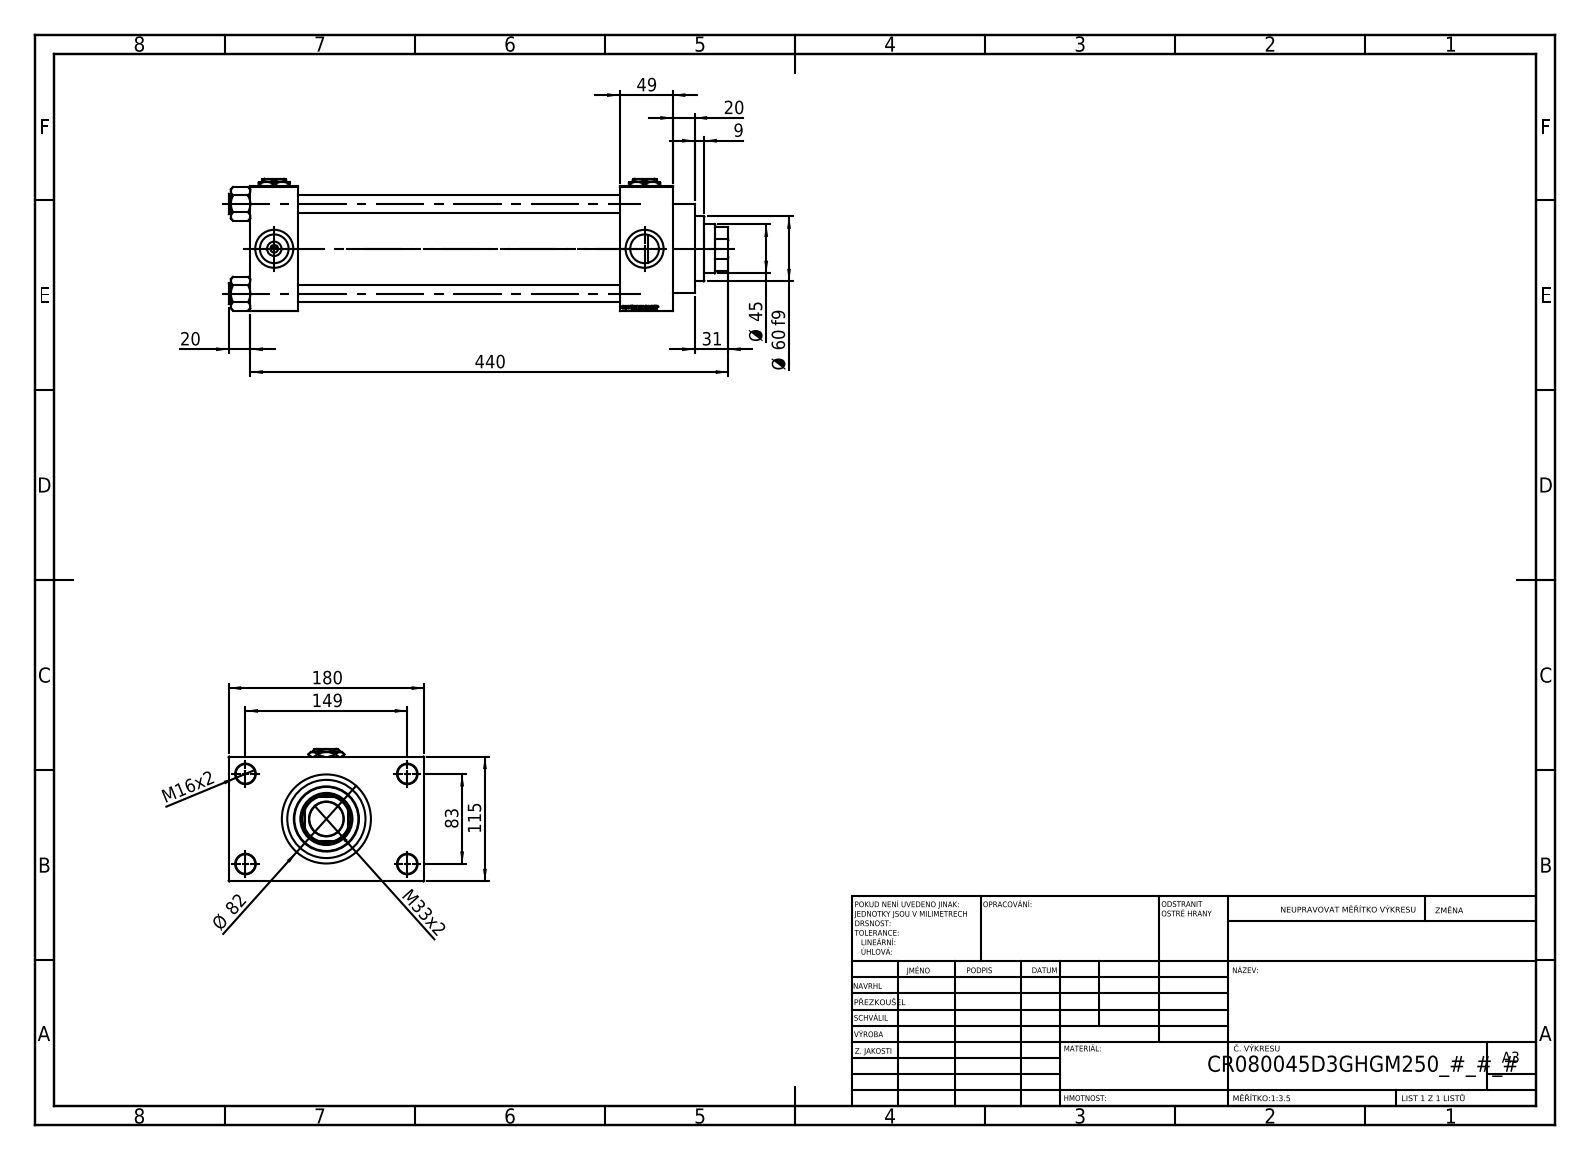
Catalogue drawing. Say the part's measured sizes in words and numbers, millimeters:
The part is named "V215_VC_A; Zatka_pro_OIL_PORT; V215CR_VCP_D; NUT_M5_D (+2 more)". Its 3-D file was written by "SolidWorks 2019 (CONFIG_CONTROL_DESIGN)". It is 13 solids with 1252 faces: 593 planar, 99 cylindrical and 560 other. Overall it measures 460 by 180 by 122 millimeters. Its volume is 2 721 000 cubic millimeters and its surface area 507 865 square millimeters. Round holes: 4 of diameter 16, 4 of diameter 18, 4 of diameter 26.44, 4 of diameter 35, 3 of diameter 7, 1 of diameter 31.5, 1 of diameter 45, 1 of diameter 48, 1 of diameter 61, 1 of diameter 72, 1 of diameter 80. Round bosses or shafts: 4 of diameter 19, 1 of diameter 86, 1 of diameter 82, 1 of diameter 60. Partial cylindrical surfaces (rounded edges, fillets, slot ends): 1 of radius 22. The main face-to-face distances are 115, 296, 345, 49, 44, 340, 389, 32.5, 147.5, 180. The hole center spacings are 33.15, 58.48, 82.7, 85.28, 89.24, 115.85, 142.43, 83.
